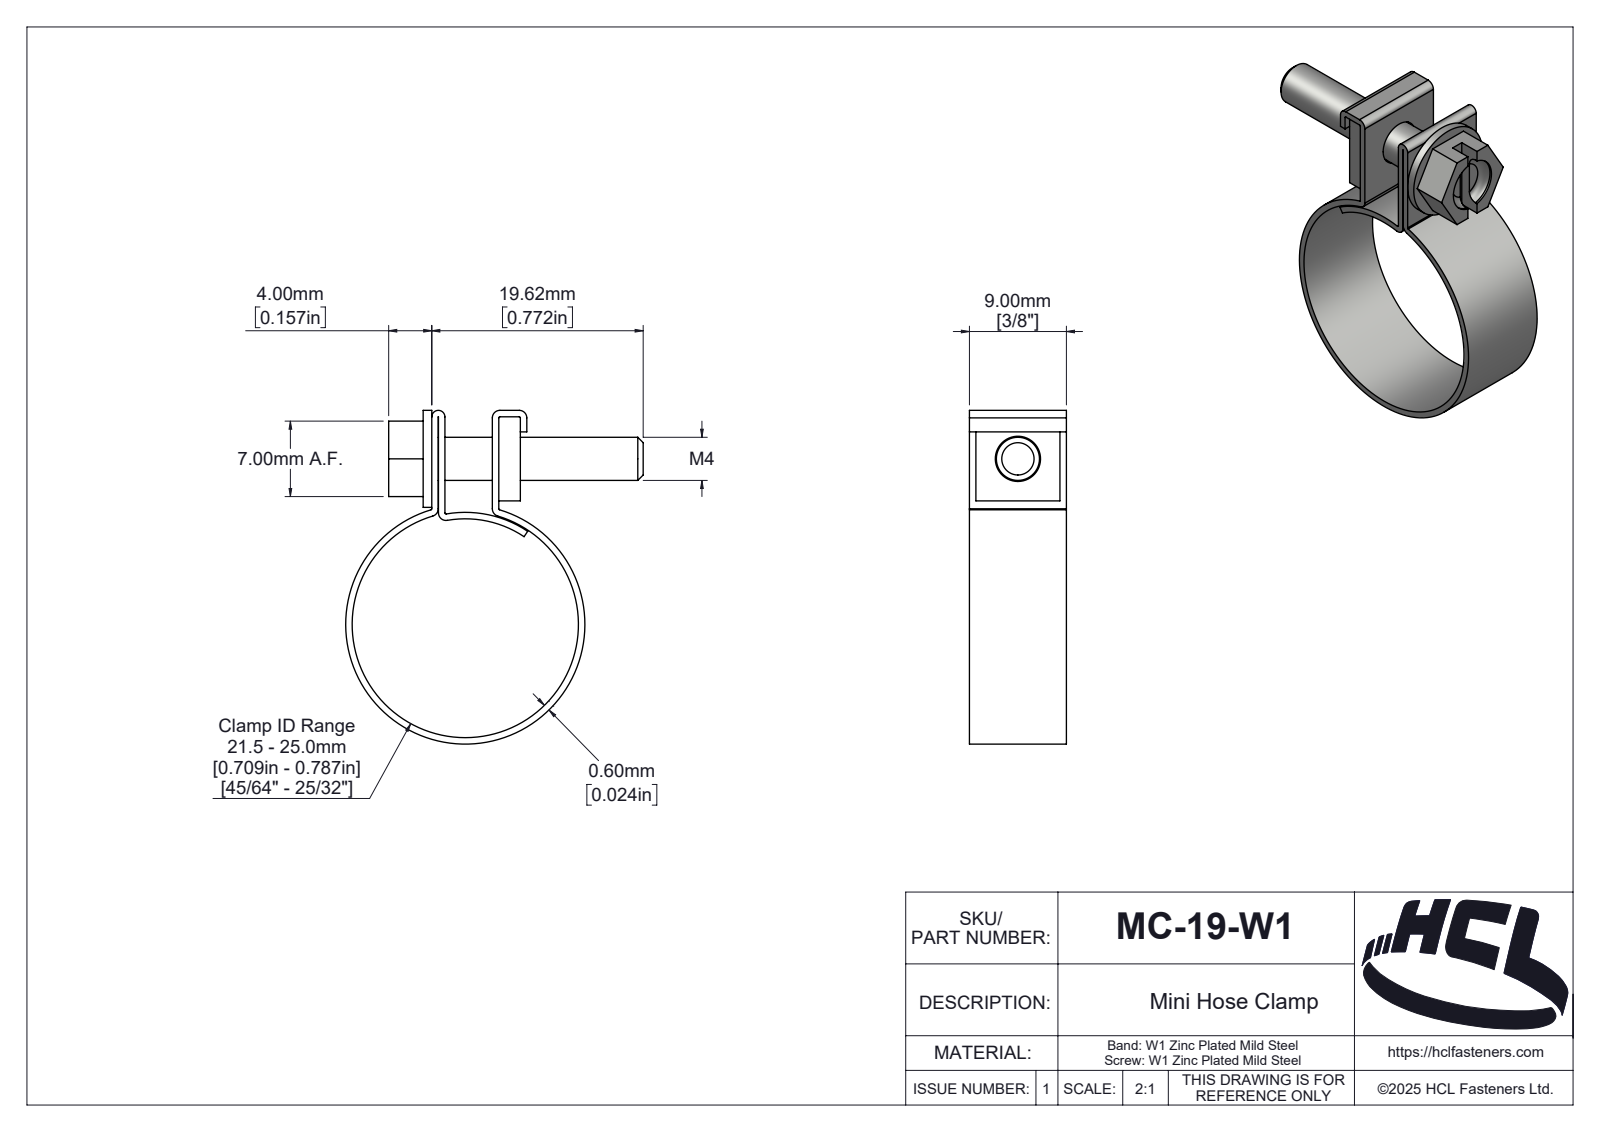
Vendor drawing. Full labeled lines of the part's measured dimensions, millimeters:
Part name (STEP PRODUCT): MC-19-W1
STEP written by: SolidWorks 2025 (AUTOMOTIVE_DESIGN)
Units: millimetres
Bodies: 3 solids, 175 faces (38 planar, 84 cylindrical, 53 other)
Overall size (bounding box): 30.96 × 27.61 × 9
Volume: 1 023 mm³ · Surface area: 2 592 mm²
Round holes (diameter × count): ⌀4.2 ×1, ⌀5 ×1, ⌀21 ×1
Round bosses / shafts (diameter × count): ⌀22.2 ×1, ⌀9 ×1, ⌀4 ×1
Partial cylindrical surfaces — rounded edges, fillets, slot ends (radius × count): R0.1 ×5, R0.7 ×5, R0.2 ×1, R0.61 ×1, R0.81 ×1, R1.01 ×1, R1.06 ×1, R1.28 ×1
Main face-to-face distances: 0.6, 0.62, 5, 5.62, 6.22, 7, 2, 2.6, 8.22, 7.6
